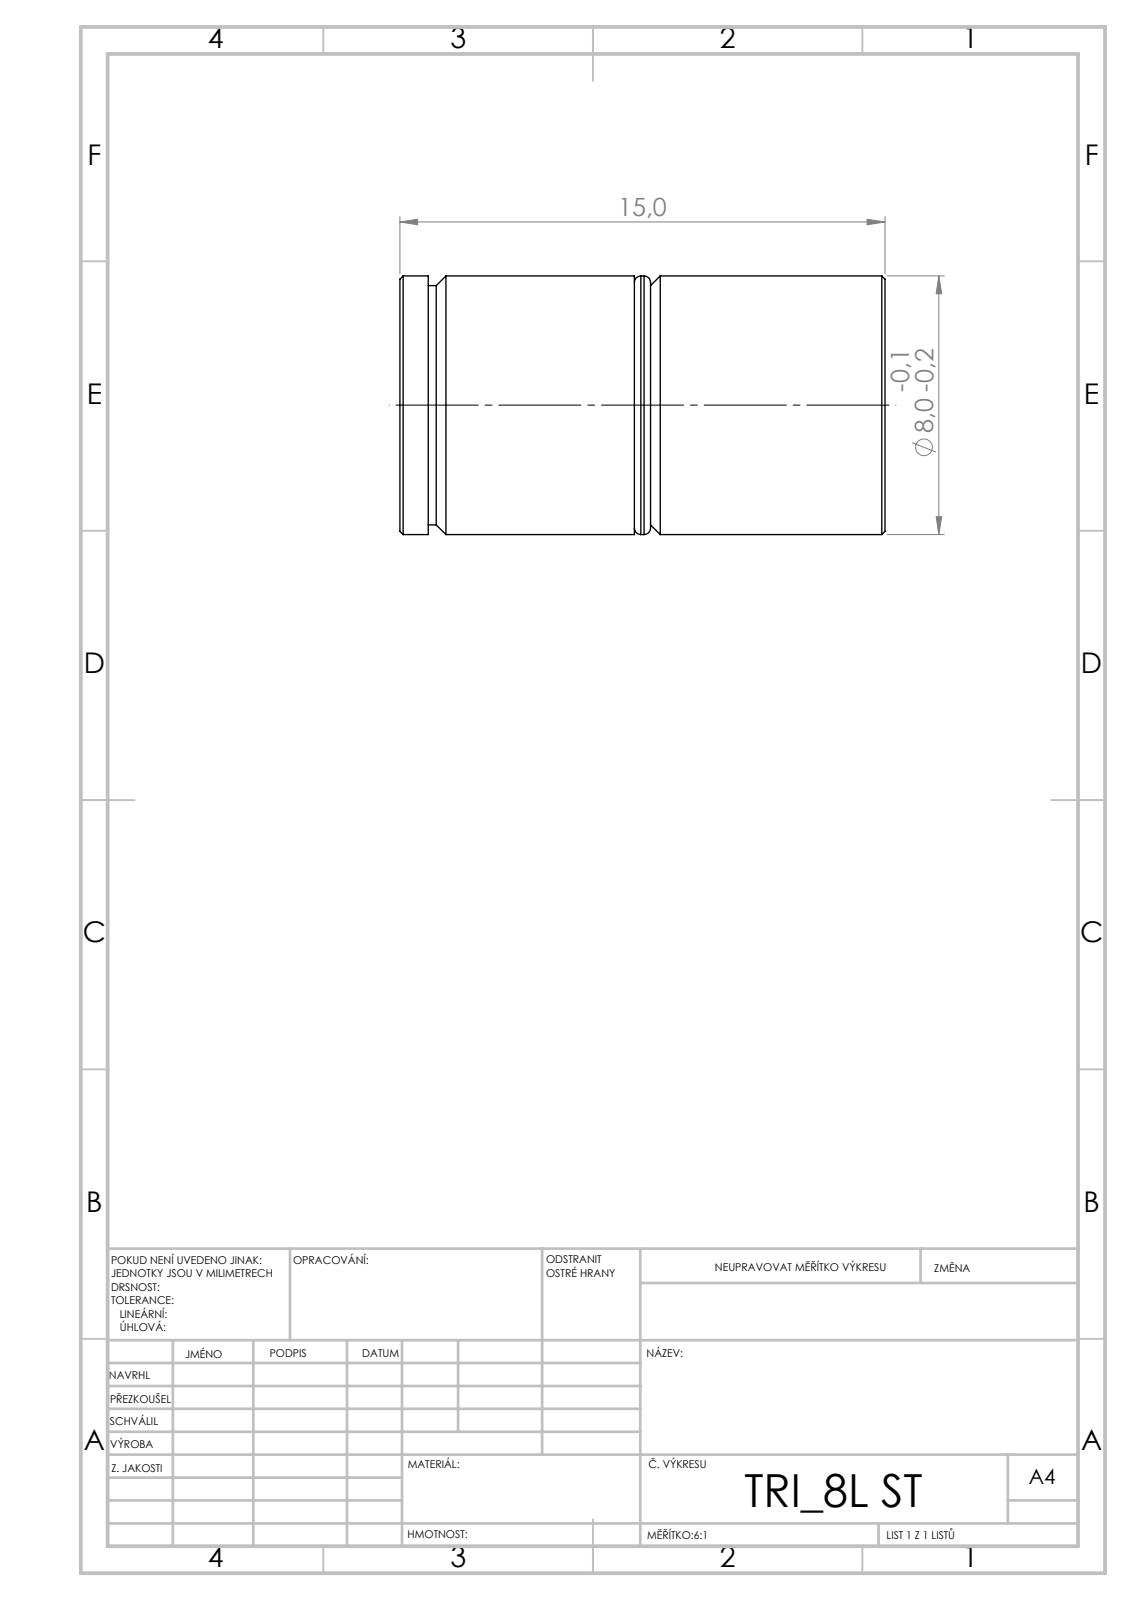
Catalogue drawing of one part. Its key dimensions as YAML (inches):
step_written_by: "SolidWorks 2019 (CONFIG_CONTROL_DESIGN)"
units: inches
bodies: {solids: 2, faces: 43, planar: 19, cylindrical: 12, other: 12}
overall_size: [0.591, 0.315, 0.315]
volume: 0.045
surface_area: 0.963
round_bosses_or_shafts:
  - {diameter: 0.315, count: 1}
  - {diameter: 0.291, count: 1}
face_to_face_distances: [0.285, 0.305, 0.02, 0.246, 0.266, 0.551, 0.039, 0.591, 0.244, 0.556]
